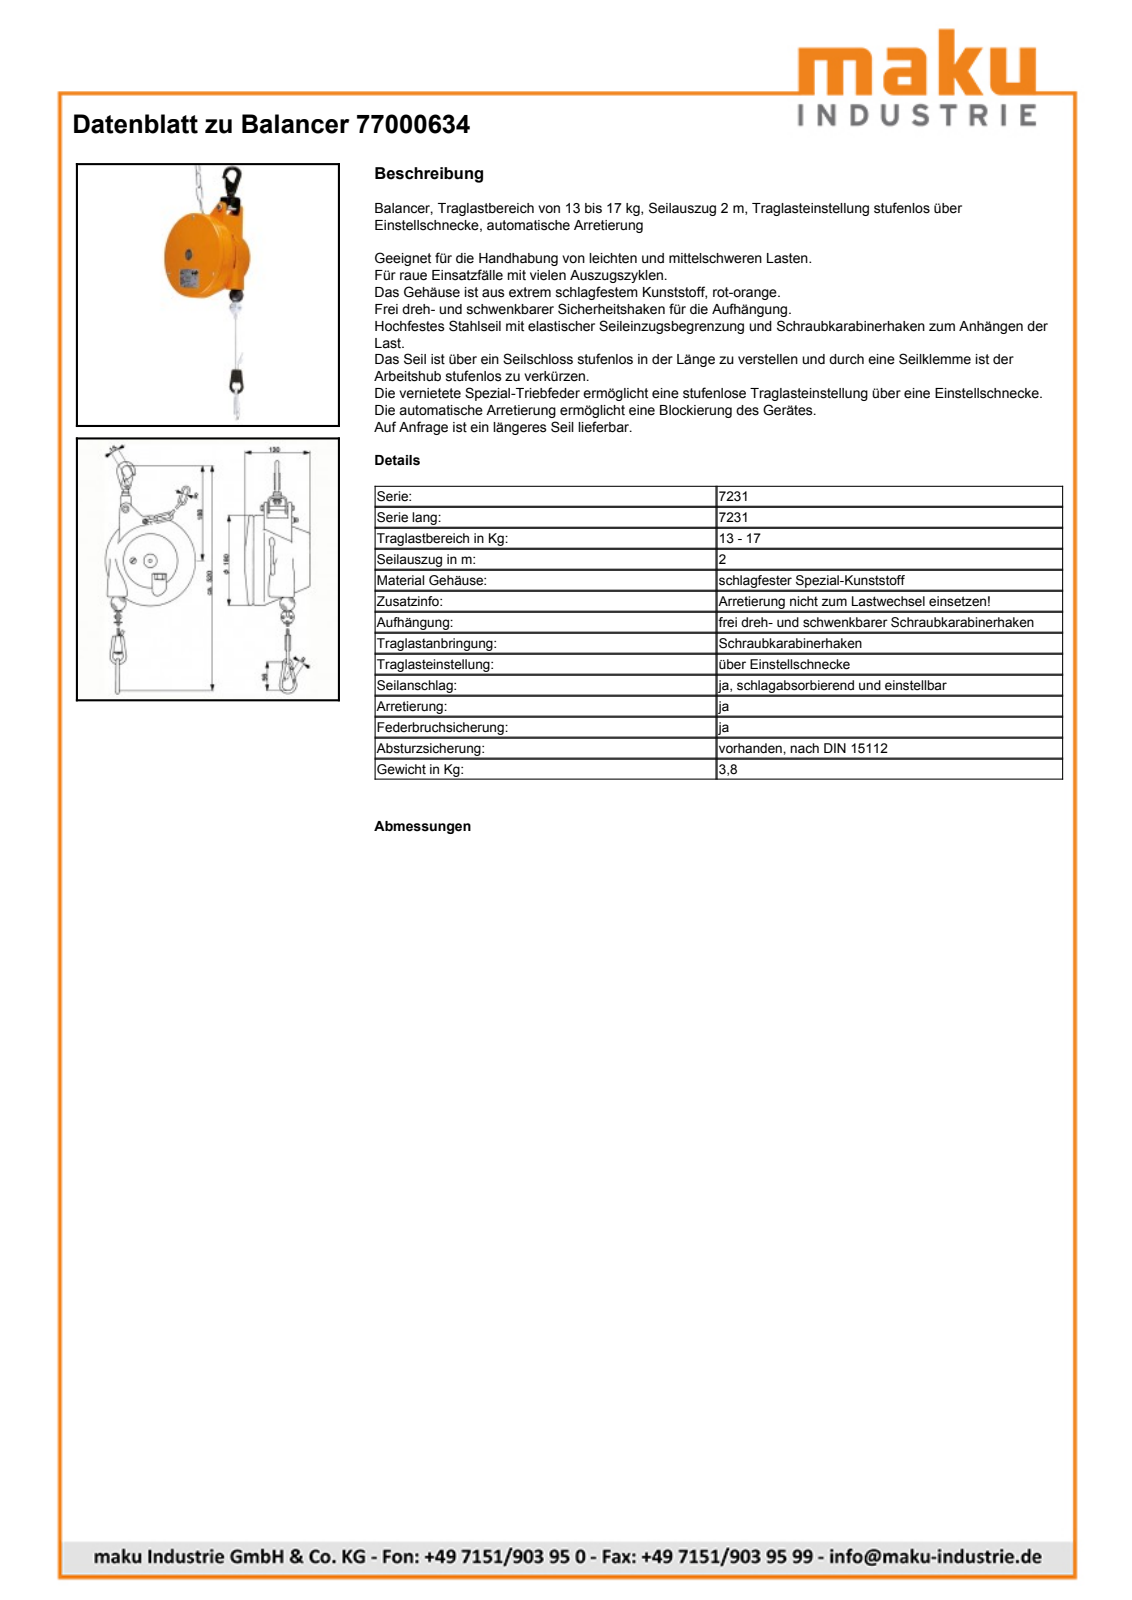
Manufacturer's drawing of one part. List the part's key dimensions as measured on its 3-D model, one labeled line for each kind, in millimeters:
Part name (STEP PRODUCT): 7230-31
STEP written by: Autodesk Inventor 2014 (AUTOMOTIVE_DESIGN)
Units: millimetres
Bodies: 23 solids, 935 faces (402 planar, 334 cylindrical, 199 other)
Overall size (bounding box): 646.34 × 180.4 × 131.6
Volume: 25 191 mm³ · Surface area: 171 541 mm²
Round holes (diameter × count): ⌀8.3 ×5, ⌀10 ×4, ⌀4 ×2, ⌀4.3 ×2, ⌀16 ×2, ⌀1.7 ×1, ⌀2 ×1, ⌀2.5 ×1, ⌀3.2 ×1, ⌀5.5 ×1, ⌀7 ×1, ⌀8.05 ×1
Round bosses / shafts (diameter × count): ⌀4 ×7, ⌀2 ×6, ⌀8 ×4, ⌀6.8 ×4, ⌀22 ×3, ⌀5 ×3, ⌀15 ×2, ⌀7 ×2
Partial cylindrical surfaces — rounded edges, fillets, slot ends (radius × count): R0.13 ×32, R0.5 ×13, R5 ×13, R0.63 ×12, R1.5 ×11, R1 ×9, R4 ×7, R3 ×6
Main face-to-face distances: 8, 131.5, 3, 36.96, 94.54, 48, 131.6, 94.64, 5, 44.96
Hole centre spacings: 33, 54.96, 57.16, 81, 110.82, 140.3, 87.47, 11.18
